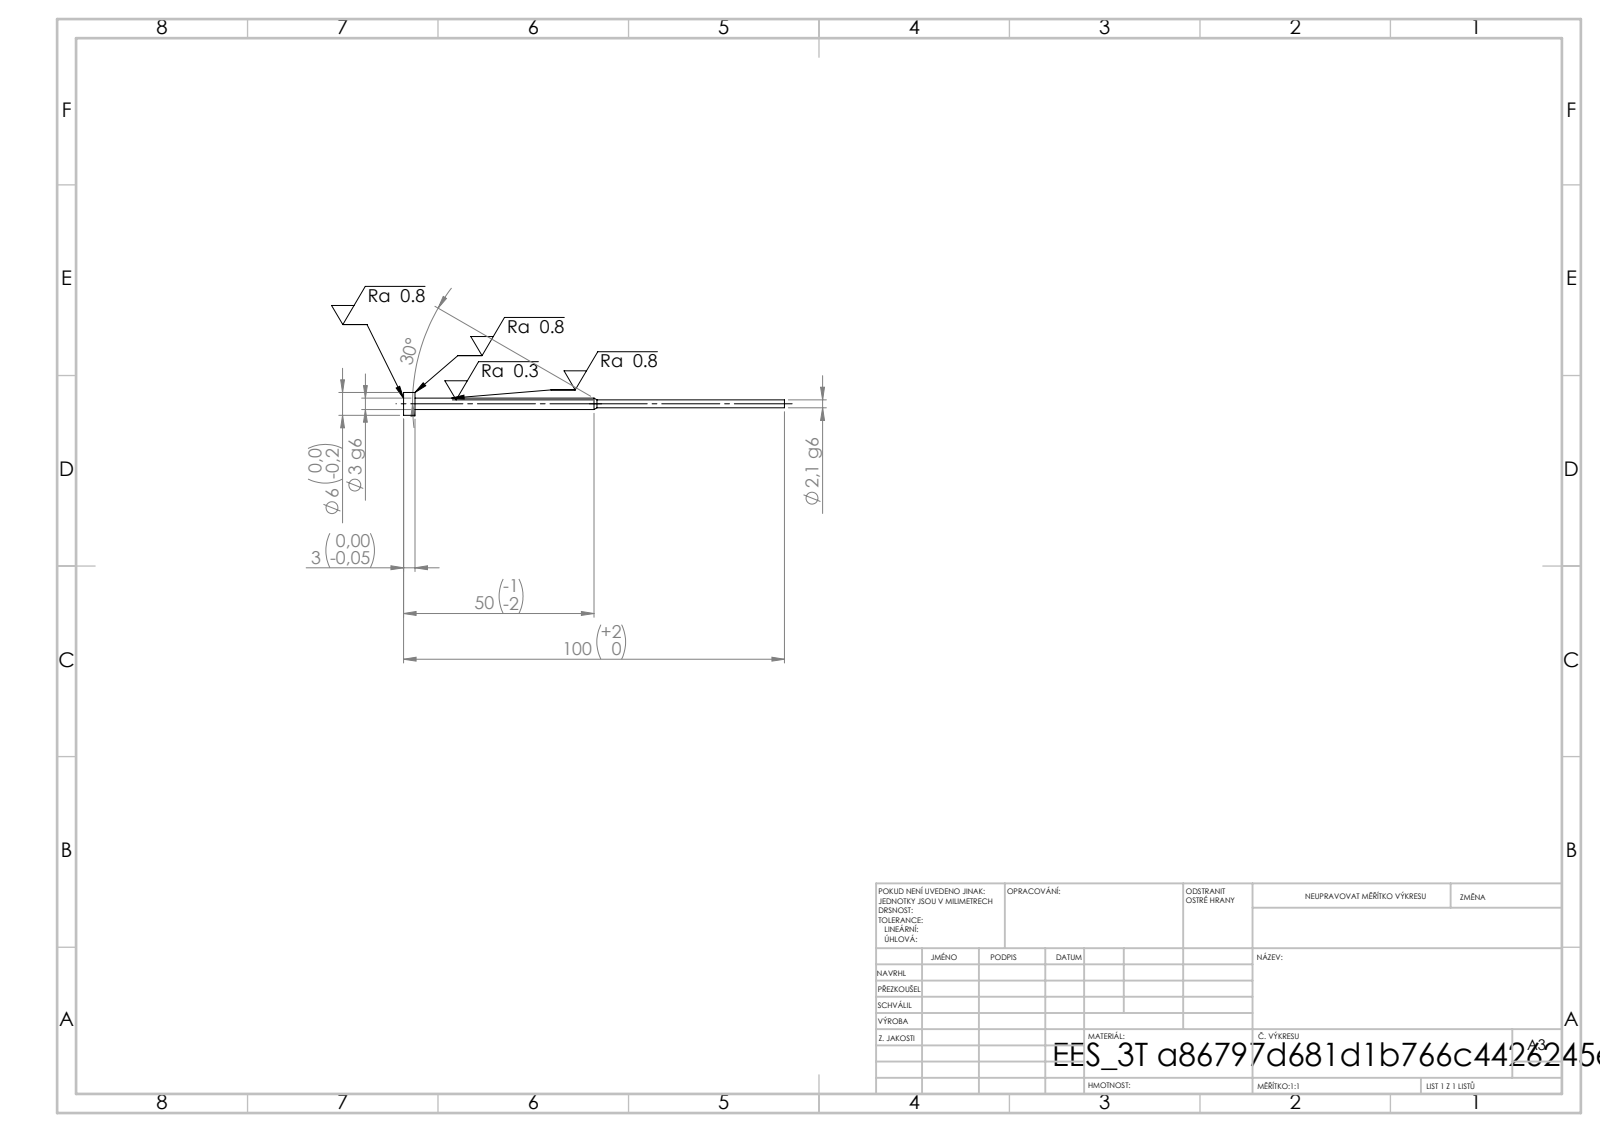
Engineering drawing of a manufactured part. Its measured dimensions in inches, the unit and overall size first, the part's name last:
Units: inches
Overall size (bounding box): 3.937 × 0.236 × 0.236
Round bosses / shafts (diameter × count): ⌀0.236 ×1, ⌀0.118 ×1, ⌀0.083 ×1
Main face-to-face distances: 0.118, 3.819, 3.937
Volume: 0.036 in³ · Surface area: 1.37 in²
Bodies: 1 solid, 11 faces (3 planar, 6 cylindrical, 2 other)
STEP written by: SolidWorks 2019 (CONFIG_CONTROL_DESIGN)
